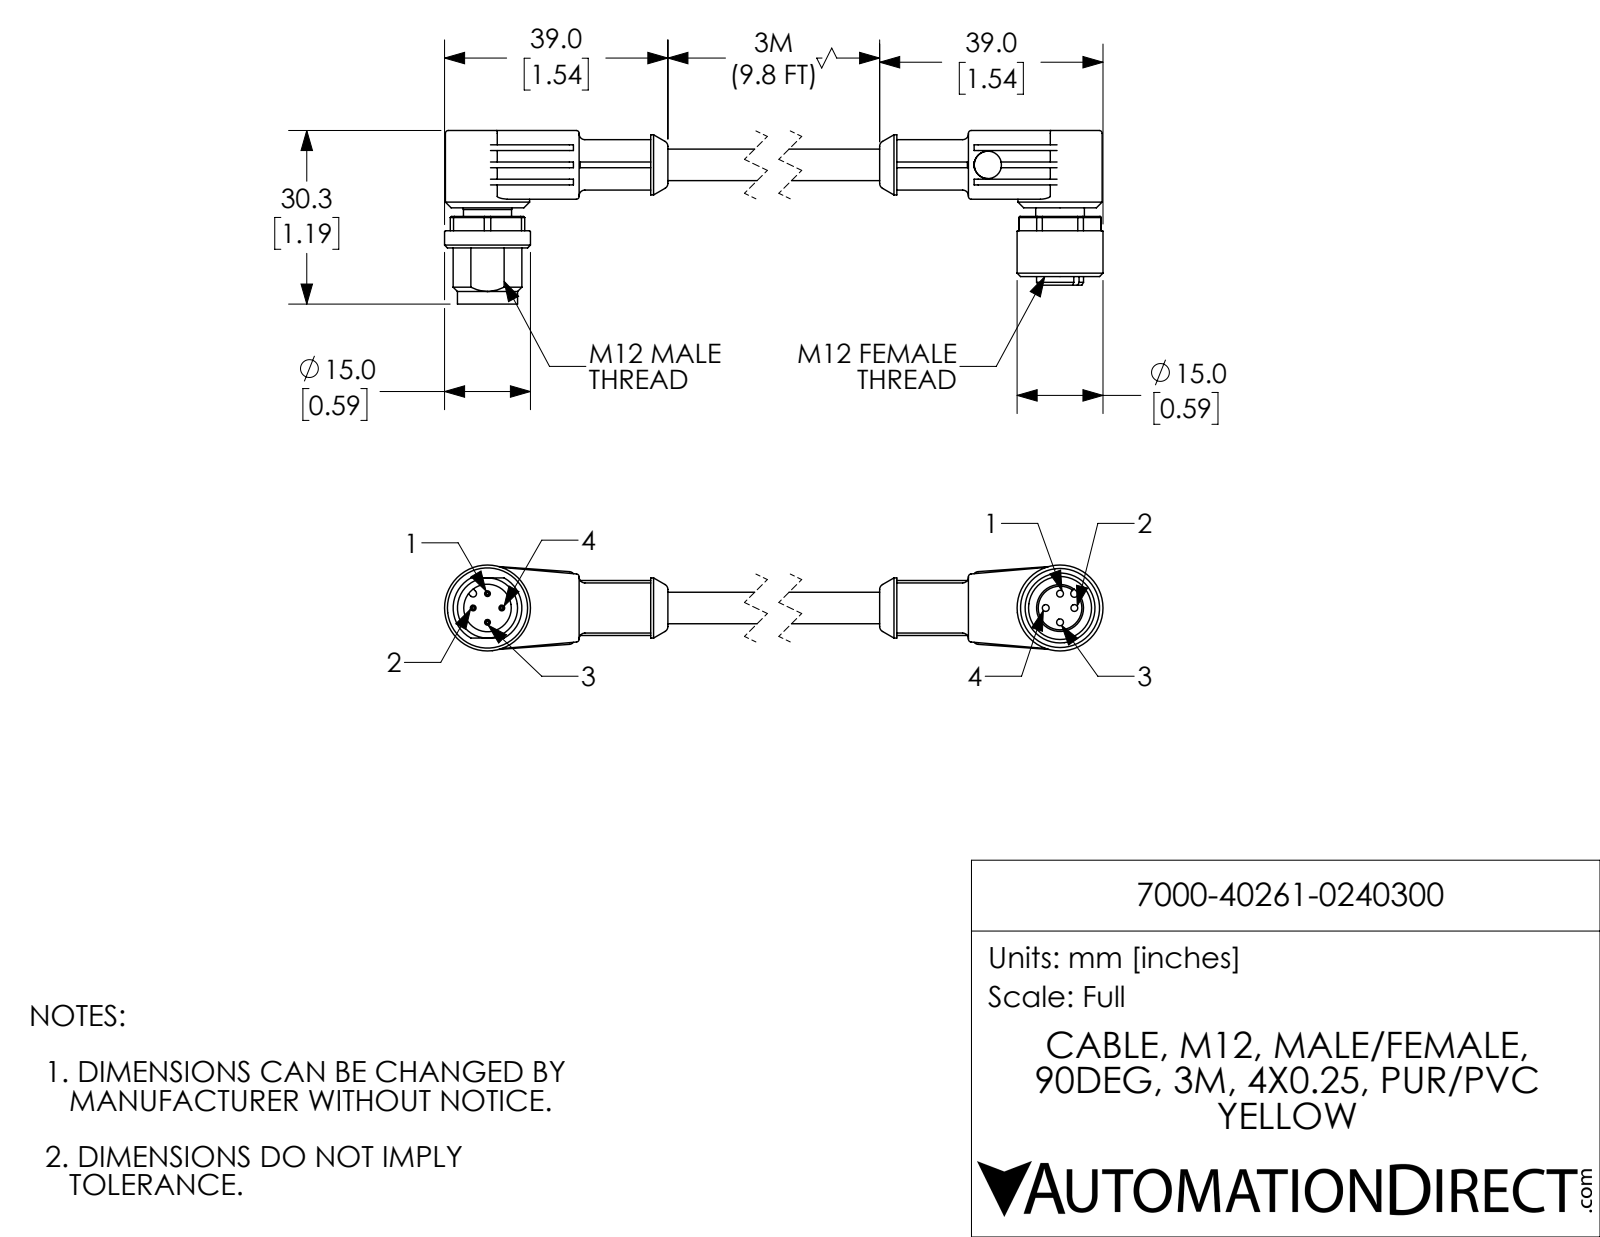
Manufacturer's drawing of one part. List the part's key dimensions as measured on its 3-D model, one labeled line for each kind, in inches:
Part name (STEP PRODUCT): 7000-40261-0240300; 7000-40261-0240300_FEMALE; 7000-40261-0240300_MALE
STEP written by: SolidWorks 2017 (AUTOMOTIVE_DESIGN)
Units: inches
Bodies: 2 solids, 290 faces (123 planar, 104 cylindrical, 63 other)
Overall size (bounding box): 5.118 × 1.193 × 0.591
Volume: 0.829 in³ · Surface area: 10.88 in²
Round holes (diameter × count): ⌀0.047 ×4, ⌀0.189 ×2, ⌀0.327 ×1, ⌀0.433 ×1
Round bosses / shafts (diameter × count): ⌀0.039 ×4, ⌀0.591 ×2, ⌀0.579 ×2, ⌀0.413 ×2, ⌀0.346 ×1, ⌀0.335 ×1, ⌀0.333 ×1, ⌀0.331 ×1
Partial cylindrical surfaces — rounded edges, fillets, slot ends (radius × count): R0.02 ×16, R0.039 ×4, R0.283 ×2, R0.024 ×1, R0.026 ×1, R0.236 ×1
Main face-to-face distances: 0.472, 0.059, 0.118, 0.591, 0.531, 0.178, 0.217, 0.098, 0.374, 0.256
Hole centre spacings: 0.098, 0.139, 0.197, 4.529, 3.563, 4.429, 4.528, 4.626
